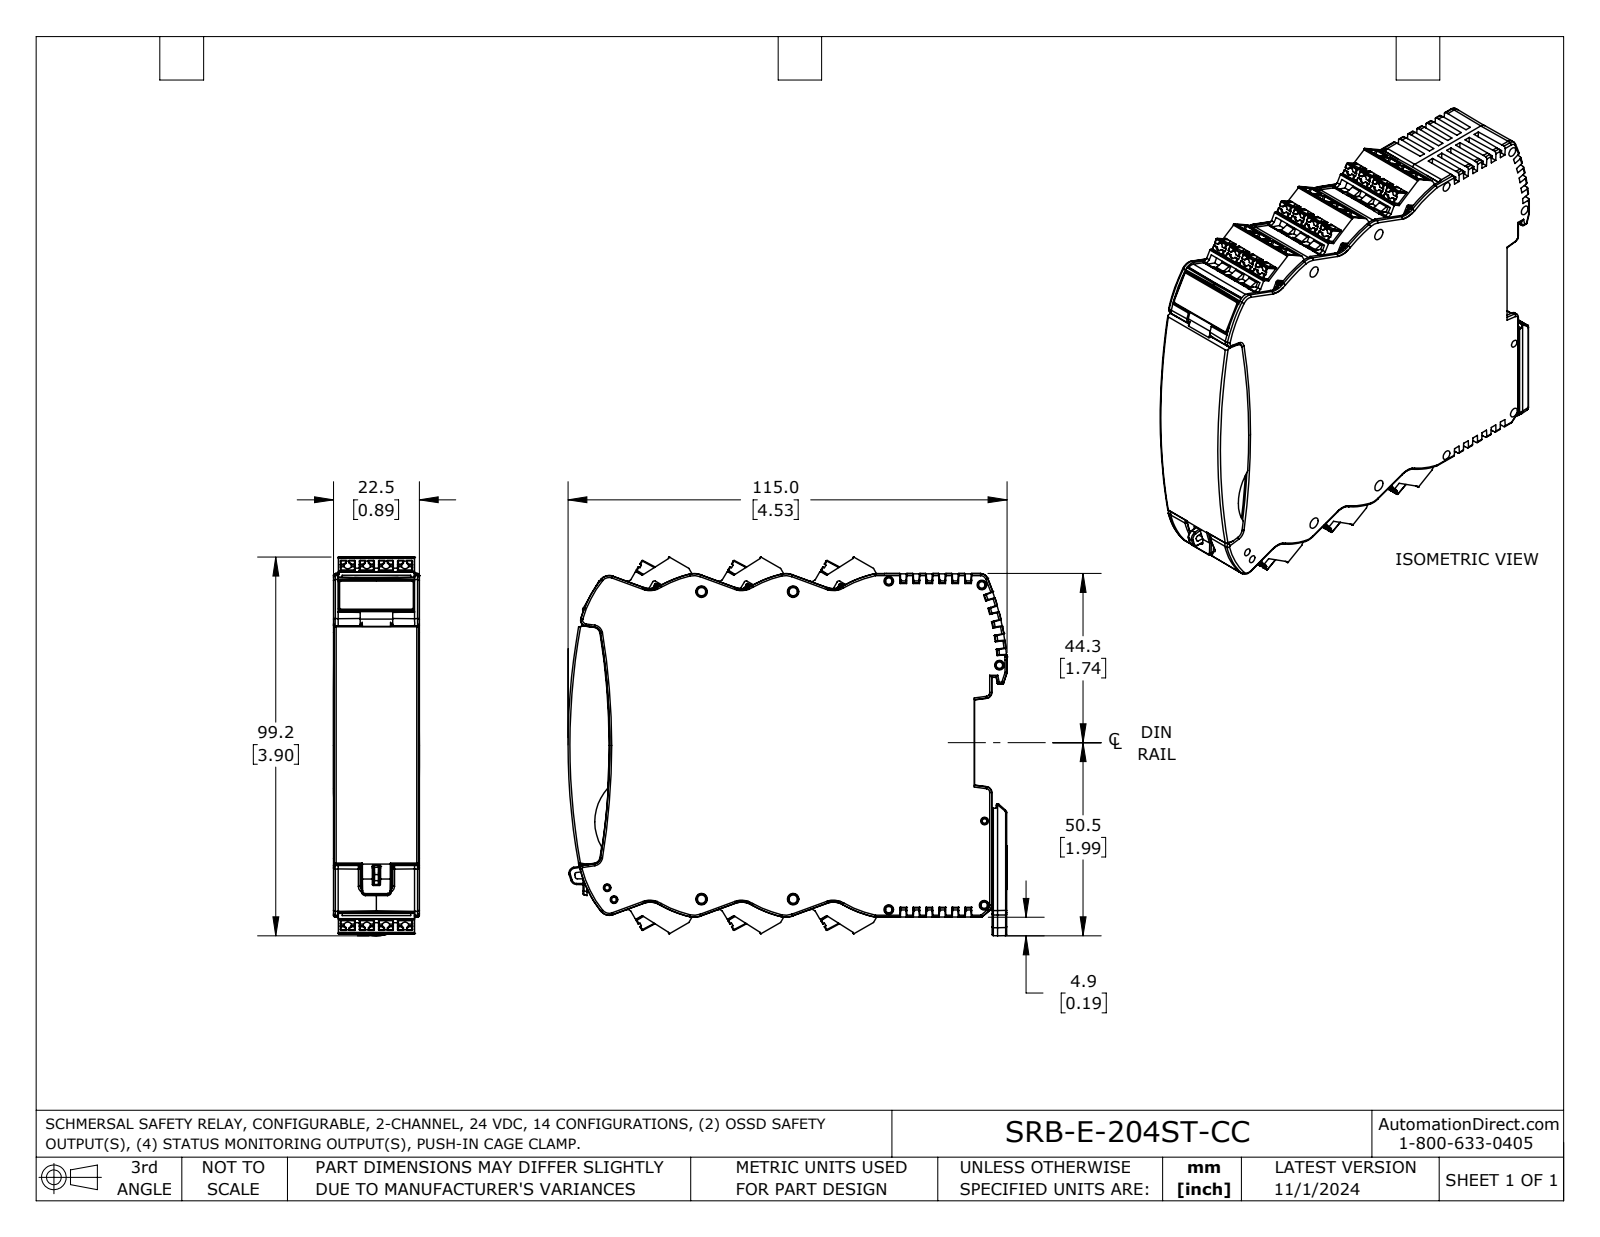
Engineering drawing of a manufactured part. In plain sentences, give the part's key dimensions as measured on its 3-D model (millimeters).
The part is named "SRB-E-204ST-CC". Its 3-D file was written by "SolidWorks 2023 (AUTOMOTIVE_DESIGN)". It is 2 solids with 5529 faces: 3184 planar, 1517 cylindrical and 828 other. Overall it measures 115 by 99.2 by 22.5 millimeters. Its volume is 213 500 cubic millimeters and its surface area 45 020 square millimeters. Round bosses or shafts: 1 of diameter 1.7. Partial cylindrical surfaces (rounded edges, fillets, slot ends): 293 of radius 0.2, 264 of radius 0.3, 225 of radius 0.5, 66 of radius 0.1, 38 of radius 1, 36 of radius 0.3, 24 of radius 1.2, 24 of radius 1.5. The main face-to-face distances are 22.5, 3.4, 5, 1.3, 3.1, 6.8, 1.3, 19.9, 0.9, 3.4.
